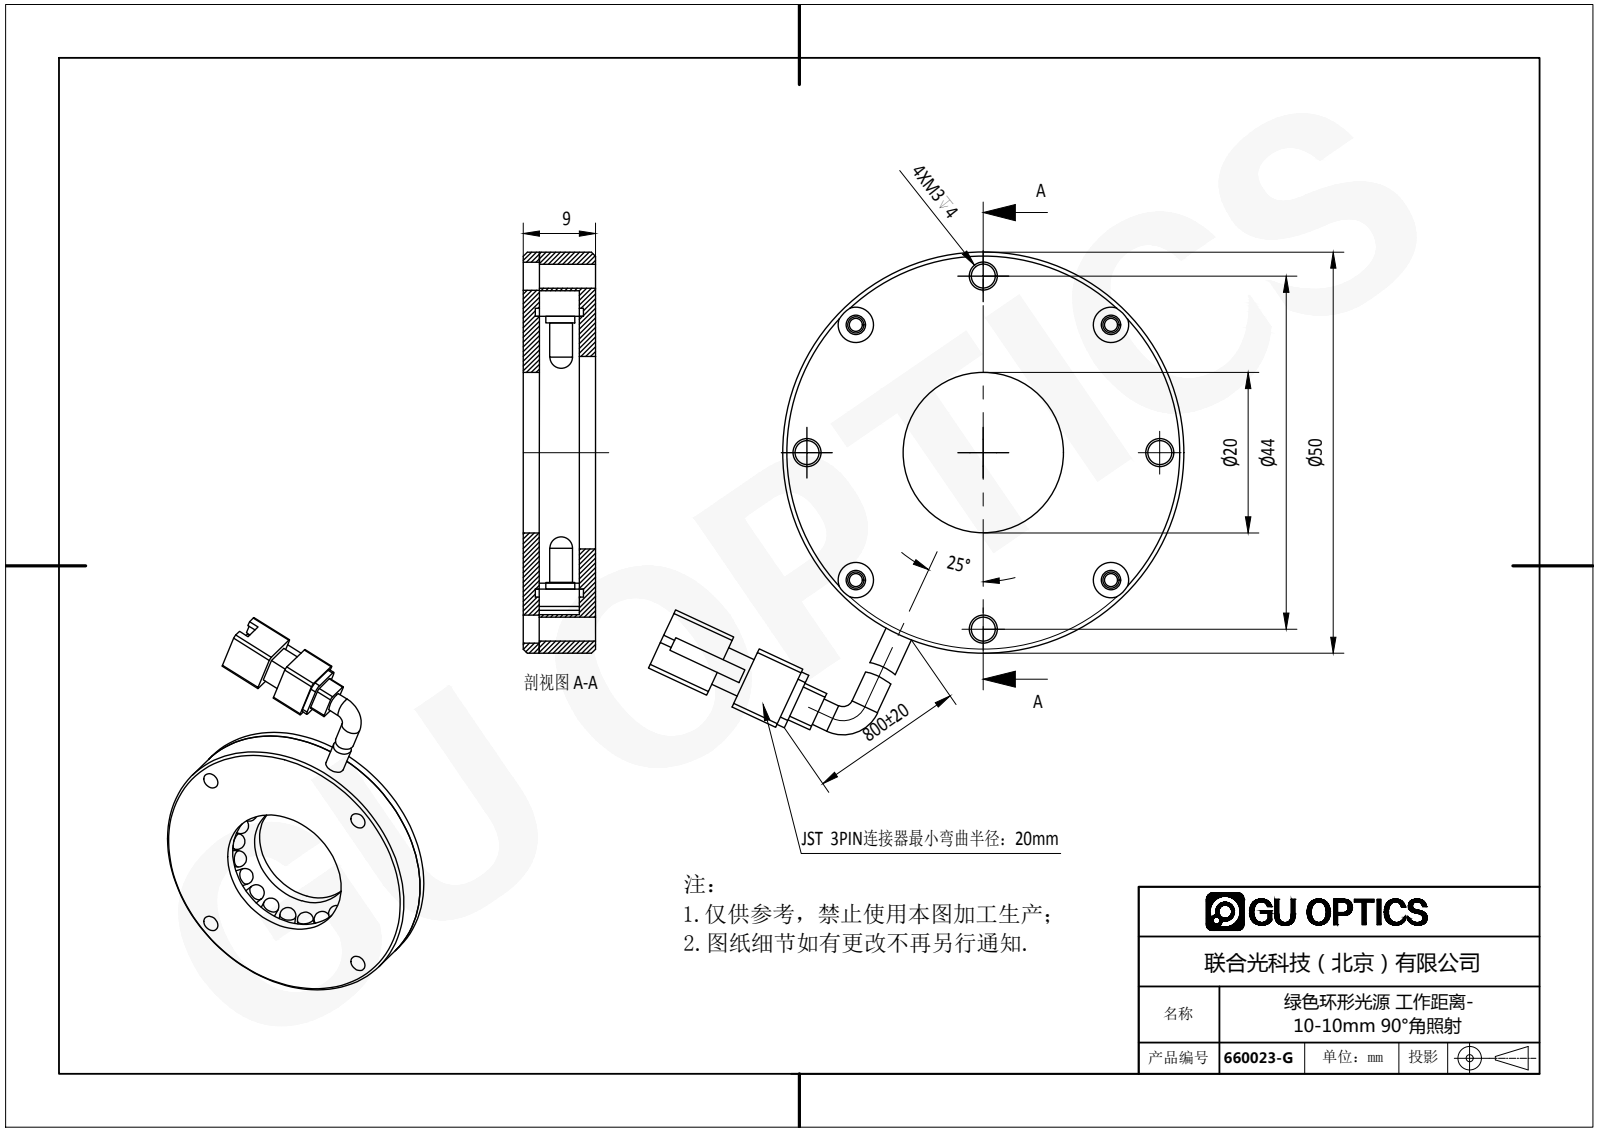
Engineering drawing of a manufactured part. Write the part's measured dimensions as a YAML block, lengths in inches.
part_name: "660023-G"
step_written_by: "SolidWorks 2016 (AUTOMOTIVE_DESIGN)"
units: inches
bodies: {solids: 26, faces: 561, planar: 329, cylindrical: 187, other: 45}
overall_size: [2.894, 1.969, 0.394]
volume: 0.687
surface_area: 20.77
round_holes:
  - {diameter: 0.118, count: 5}
  - {diameter: 0.138, count: 5}
  - {diameter: 0.063, count: 4}
  - {diameter: 0.079, count: 4}
  - {diameter: 0.094, count: 4}
  - {diameter: 0.787, count: 1}
  - {diameter: 0.945, count: 1}
  - {diameter: 1.417, count: 1}
  - {diameter: 1.591, count: 1}
round_bosses_or_shafts:
  - {diameter: 0.15, count: 21}
  - {diameter: 0.118, count: 21}
  - {diameter: 0.138, count: 2}
  - {diameter: 1.969, count: 1}
  - {diameter: 1.354, count: 1}
  - {diameter: 1.339, count: 1}
partial_cylinders:
  - {radius: 0.02, count: 12}
  - {radius: 0.039, count: 4}
face_to_face_distances: [0.276, 0.079, 0.354, 0.197, 0.02, 0.039, 0.217, 0.059, 0.236, 0.295]
hole_center_spacings: [0.671, 0.886, 1.253, 1.619, 1.619, 0.67, 0.866, 0.867]
